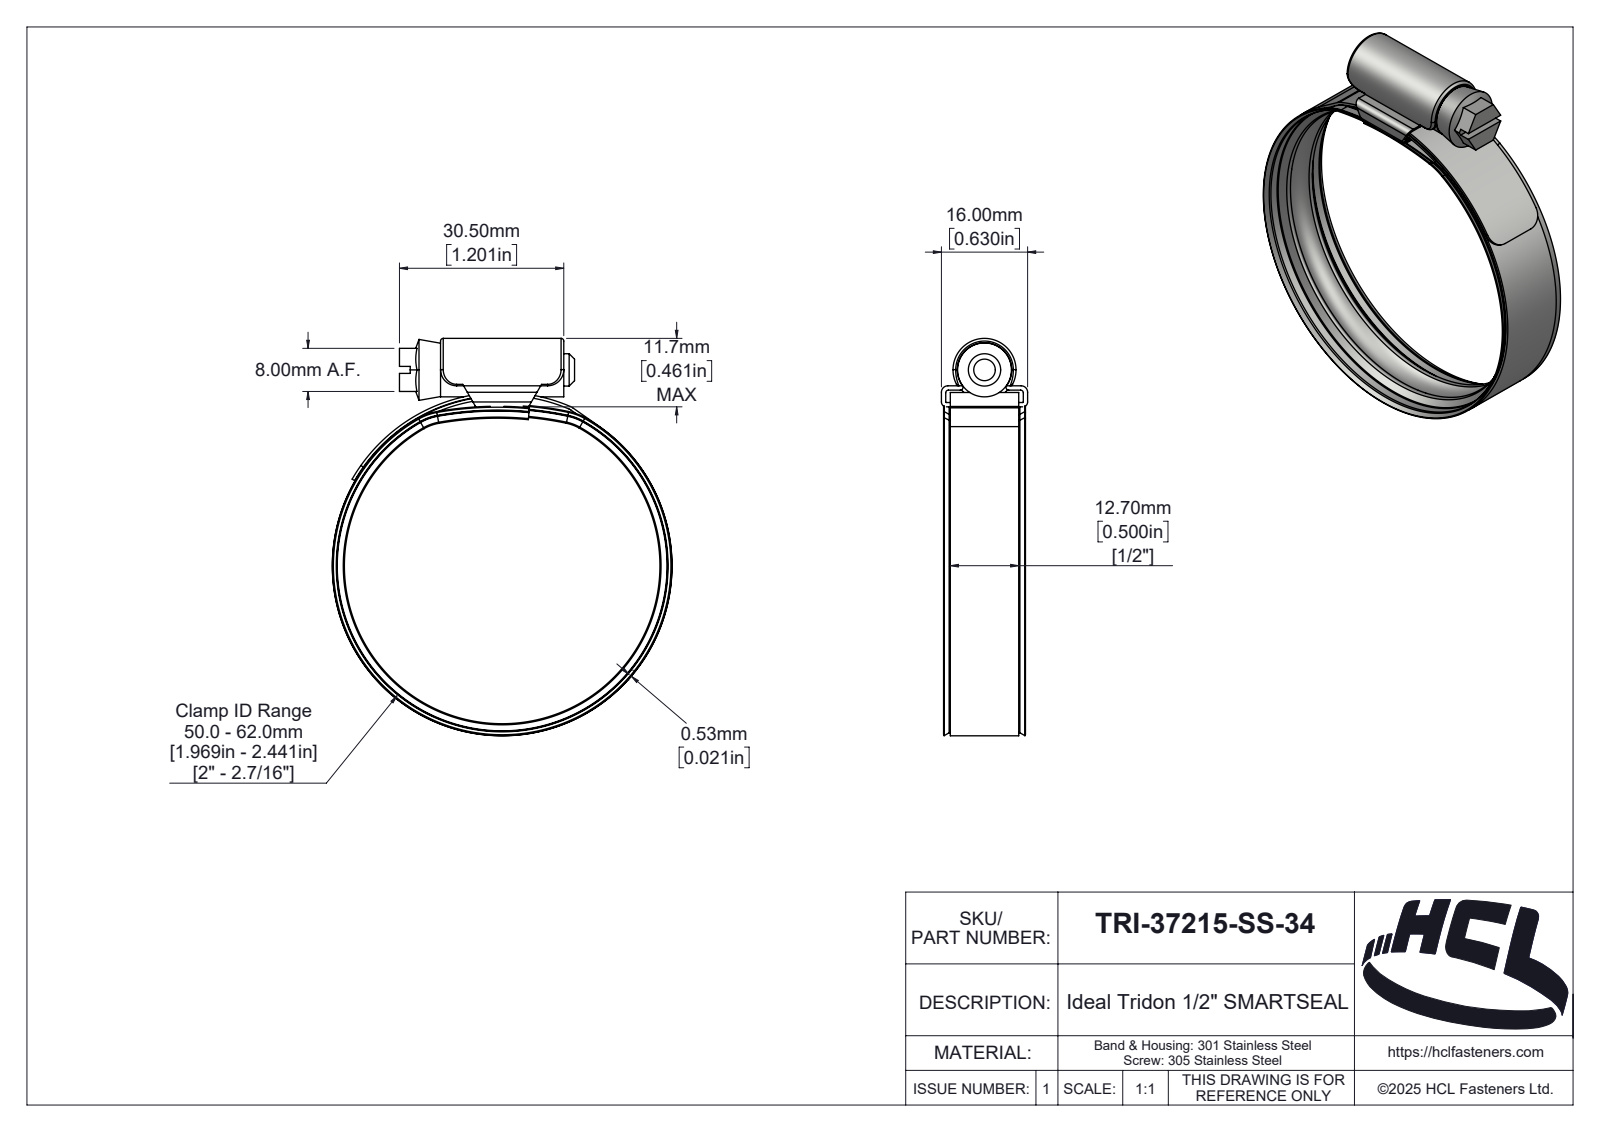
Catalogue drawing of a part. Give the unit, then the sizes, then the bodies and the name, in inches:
Units: inches
Overall size (bounding box): 2.903 × 2.483 × 0.63
Round holes (diameter × count): ⌀2.417 ×1, ⌀2.441 ×1
Round bosses / shafts (diameter × count): ⌀2.483 ×1, ⌀2.433 ×1, ⌀0.394 ×1, ⌀0.236 ×1
Partial cylindrical surfaces — rounded edges, fillets, slot ends (radius × count): R0.02 ×6, R0.118 ×4, R0.004 ×2, R0.035 ×2, R0.047 ×2, R0.39 ×2, R0.398 ×2, R0.018 ×1
Main face-to-face distances: 0.031, 0.122, 0.5, 0.021, 0.091, 1.201, 0.154, 0.065, 0.565, 0.598
Volume: 0.322 in³ · Surface area: 24.66 in²
Bodies: 4 solids, 418 faces (42 planar, 119 cylindrical, 257 other)
Part name (STEP PRODUCT): TRI-37215-SS-34
STEP written by: SolidWorks 2025 (AUTOMOTIVE_DESIGN)
